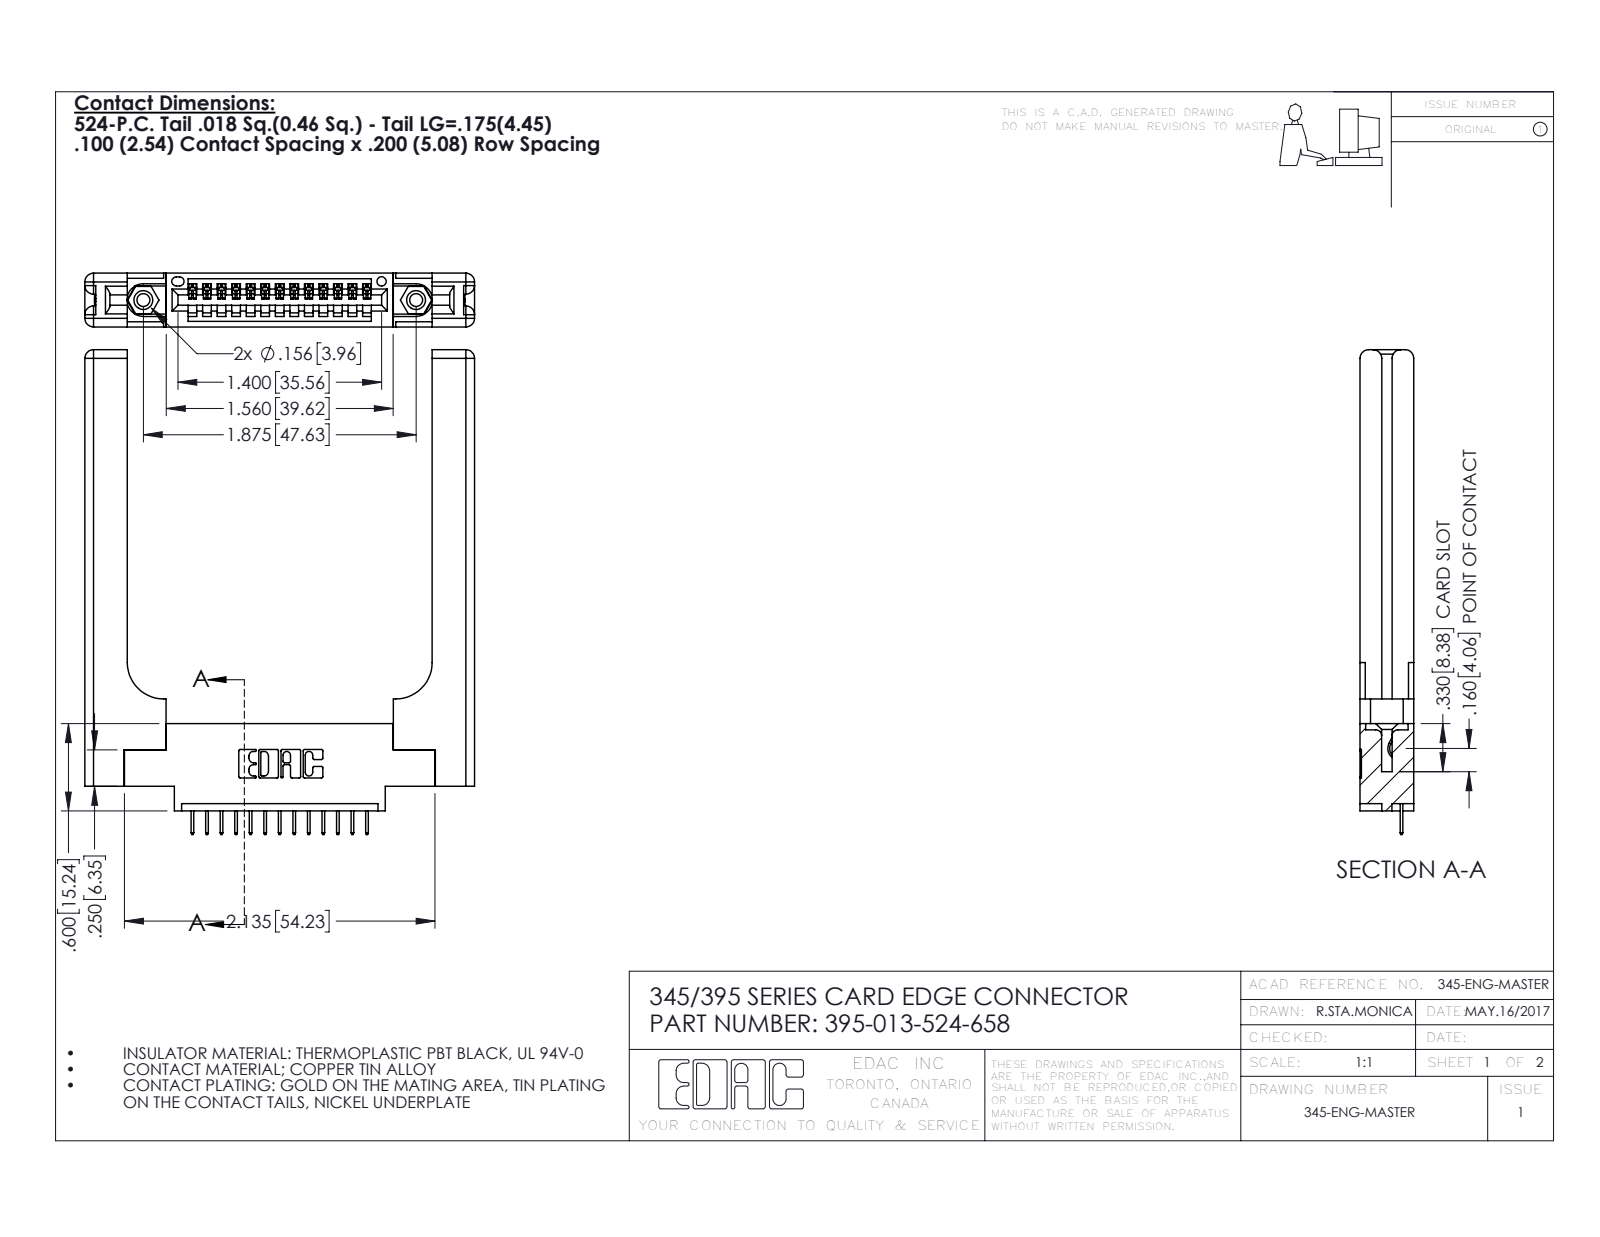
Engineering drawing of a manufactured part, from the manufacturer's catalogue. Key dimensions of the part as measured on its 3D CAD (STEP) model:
Part name (STEP PRODUCT): 345-250-001_345-250-001-102; 345-292-001_345-293-124; 345-220-058_345-220-058; 395-013-524-658 (+1 more)
STEP written by: SolidWorks 2016 (CONFIG_CONTROL_DESIGN)
Units: inches
Bodies: 18 solids, 1192 faces (830 planar, 302 cylindrical, 60 other)
Overall size (bounding box): 3.332 × 2.679 × 0.37
Volume: 0.889 in³ · Surface area: 20.04 in²
Round holes (diameter × count): ⌀0.089 ×2, ⌀0.125 ×2, ⌀0.156 ×2, ⌀0.064 ×1
Round bosses / shafts (diameter × count): ⌀0.155 ×2
Partial cylindrical surfaces — rounded edges, fillets, slot ends (radius × count): R0.006 ×26, R0.01 ×22, R0.06 ×16, R0.007 ×6, R0.031 ×6, R0.026 ×3, R0.03 ×2, R0.031 ×2
Main face-to-face distances: 0.37, 0.072, 0.15, 0.148, 0.077, 0.22, 0.298, 0.12, 2.096, 0.071
Hole centre spacings: 0.27, 1.643, 1.875
